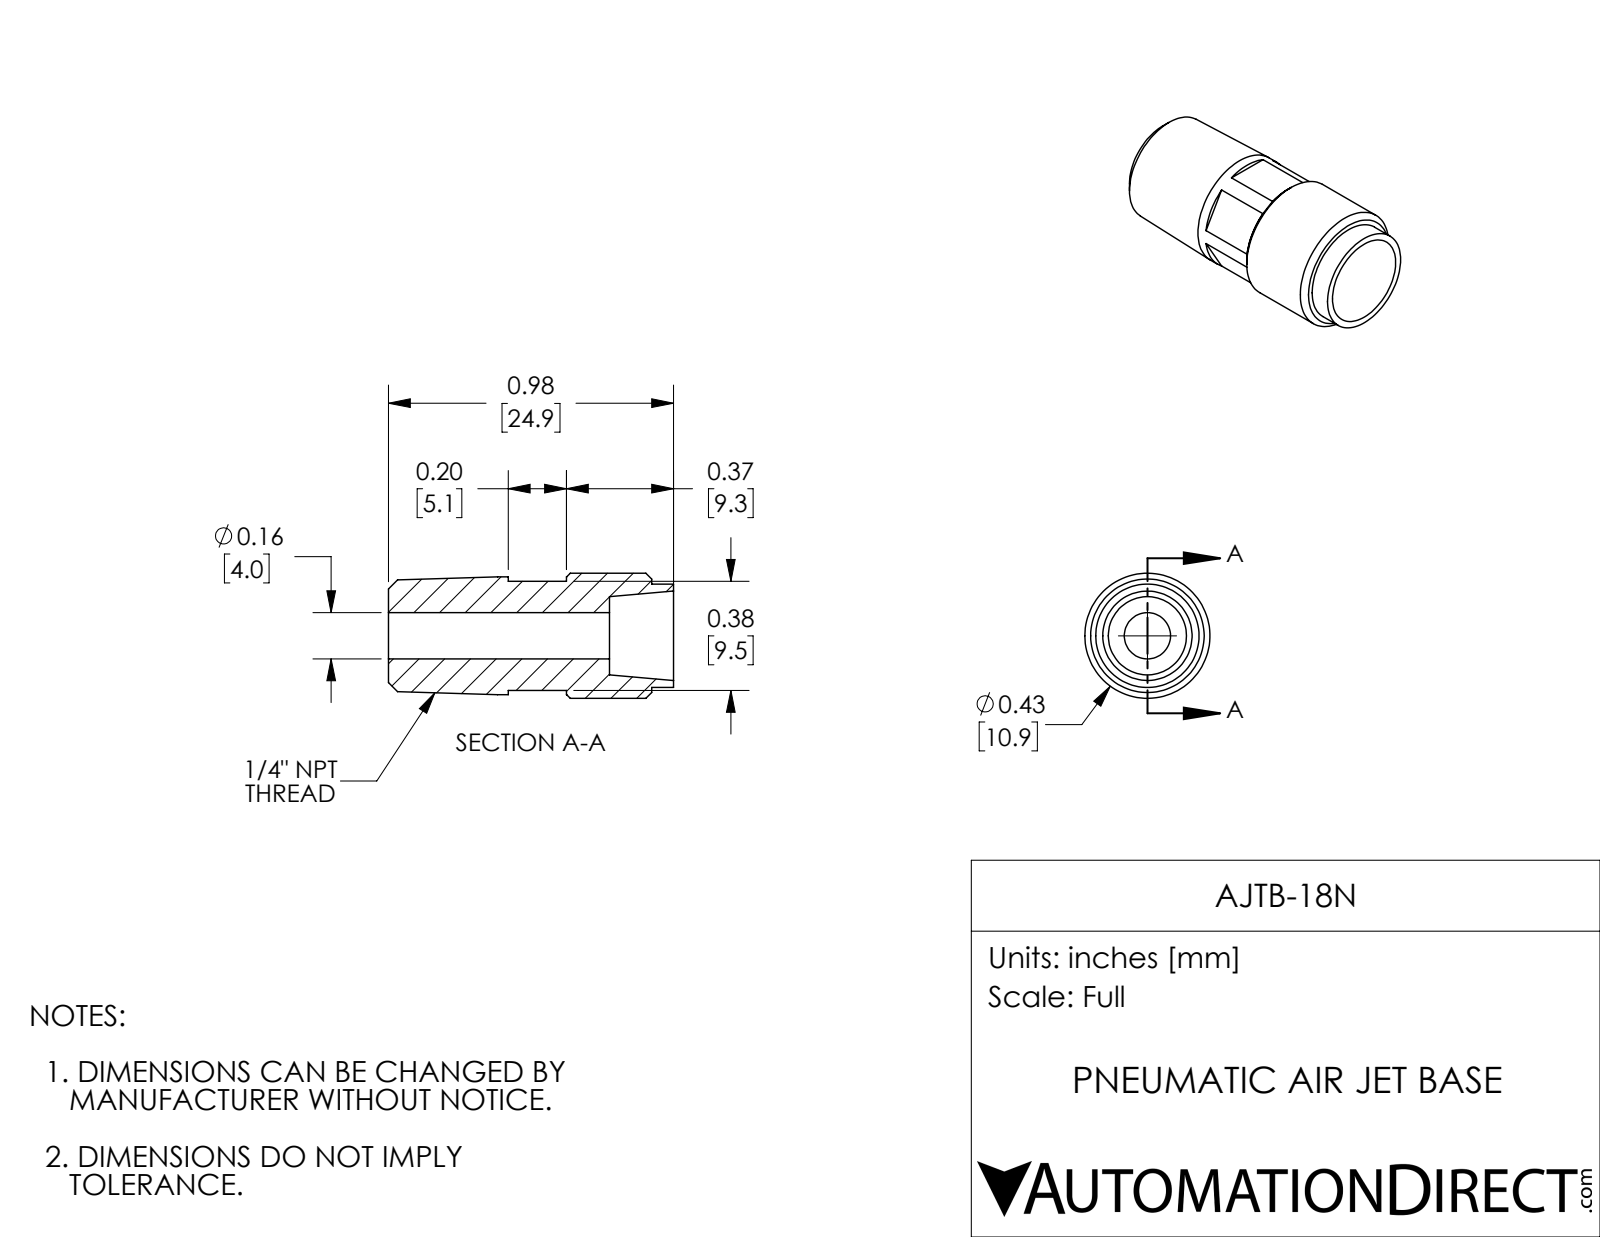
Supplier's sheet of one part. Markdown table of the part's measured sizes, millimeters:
| quantity | value |
| --- | --- |
| part name | AJTB-18N |
| STEP written by | SolidWorks 2018 (AUTOMOTIVE_DESIGN) |
| units | millimeters |
| bodies | 1 solid, 40 faces (22 planar, 8 cylindrical, 10 other) |
| overall size | 24.9 × 10.9 × 10.9 |
| volume | 1 500 mm³ |
| surface area | 1 295 mm² |
| round holes (diameter × count) | 4 × 1 |
| round bosses / shafts (diameter × count) | 10.9 × 1, 10.3 × 1, 9 × 1 |
| main face-to-face distances | 9.5, 19.3, 24.9, 5.6, 23, 3.7, 1.9, 10.5, 15.5, 5.1 |
